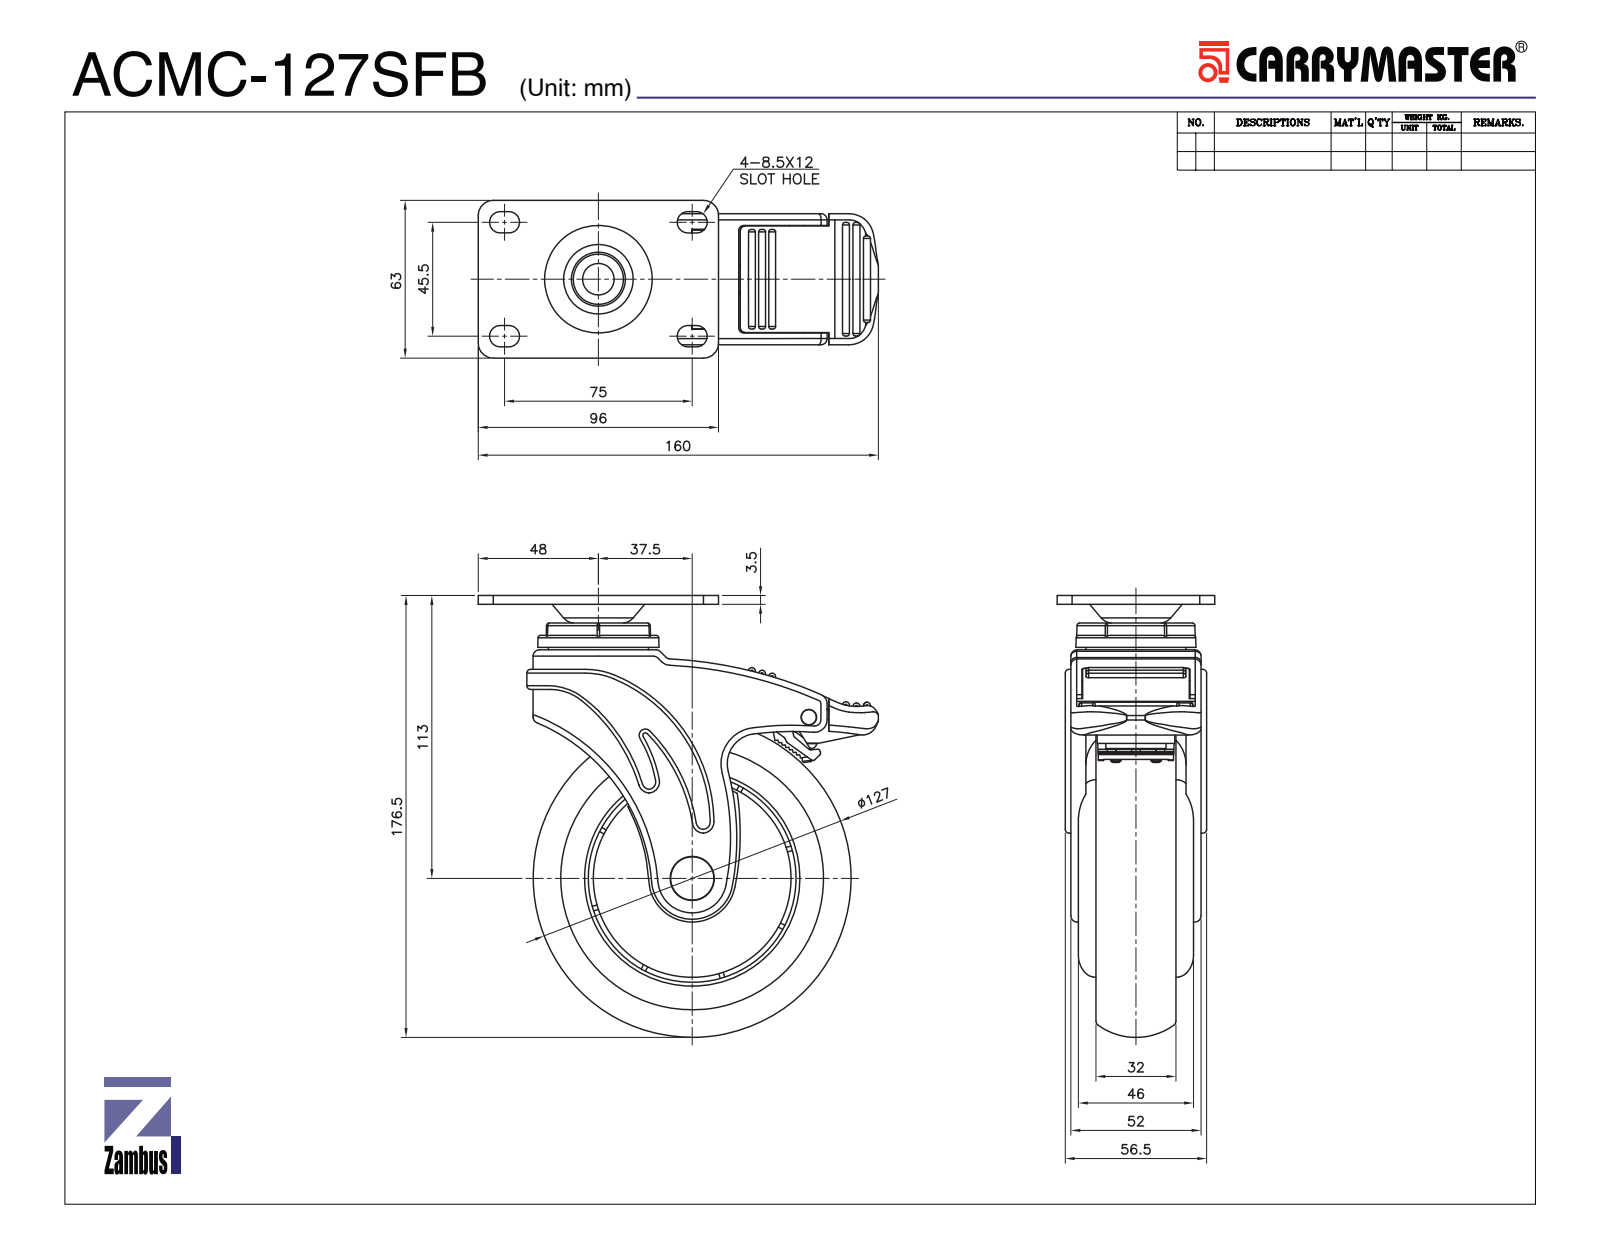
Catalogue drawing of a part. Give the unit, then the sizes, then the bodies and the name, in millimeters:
Units: millimetres
Overall size (bounding box): 176.5 × 160.64 × 63
Round holes (diameter × count): ⌀17.3 ×1, ⌀37 ×1, ⌀83 ×1, ⌀105.01 ×1
Round bosses / shafts (diameter × count): ⌀4 ×2, ⌀105 ×1, ⌀79 ×1, ⌀78.59 ×1, ⌀40 ×1, ⌀22 ×1, ⌀17 ×1, ⌀6.2 ×1
Partial cylindrical surfaces — rounded edges, fillets, slot ends (radius × count): R0.5 ×27, R1 ×16, R2 ×8, R4.25 ×8, R1.4 ×6, R2.5 ×6, R6 ×5, R4.5 ×4
Main face-to-face distances: 4.25, 36.25, 6, 10.25, 42.25, 46.5, 32, 40.5, 3.5, 4
Volume: 620 510 mm³ · Surface area: 114 170 mm²
Bodies: 6 solids, 641 faces (225 planar, 239 cylindrical, 177 other)
Part name (STEP PRODUCT): ACMC-127 TOP PLATE COVER; ACMC-127 F TOP PLATE; ACMC-127 BRAKE FRAME; ACMC-127SFB (+2 more)
STEP written by: SolidWorks 2019 (CONFIG_CONTROL_DESIGN)
